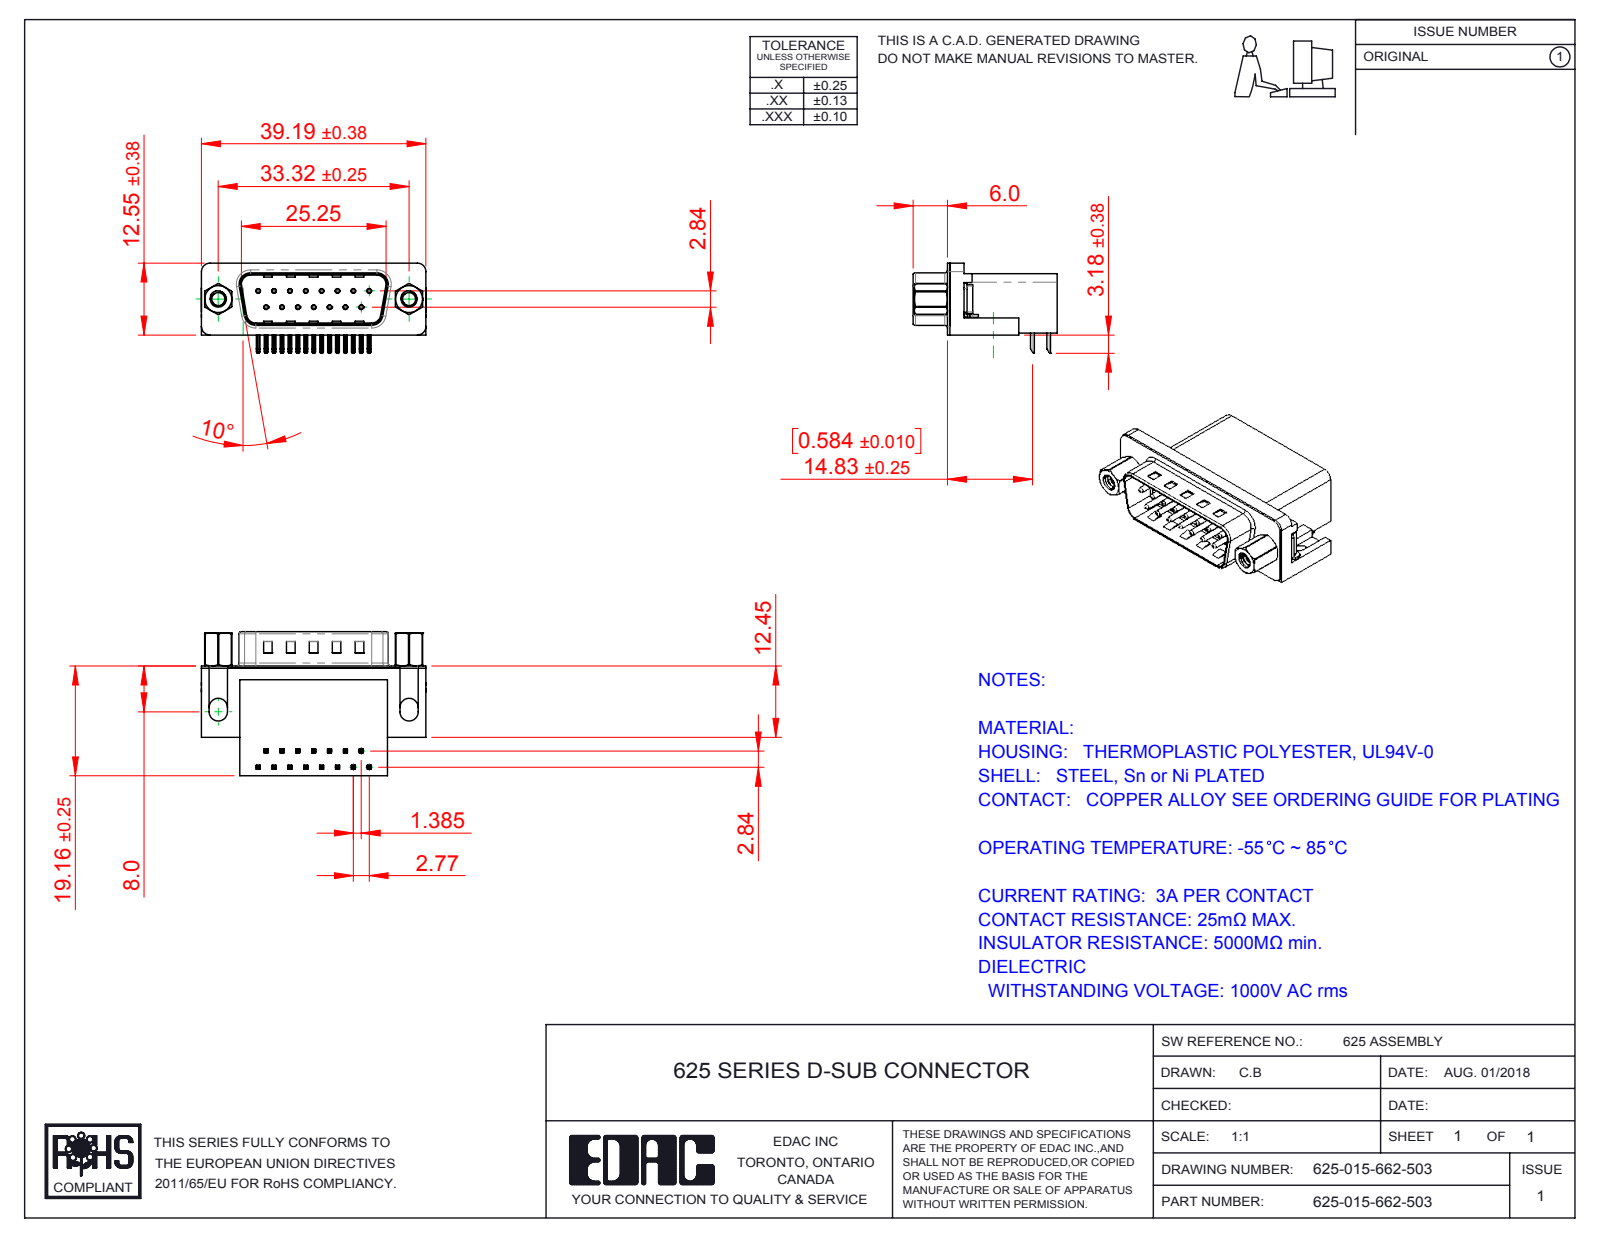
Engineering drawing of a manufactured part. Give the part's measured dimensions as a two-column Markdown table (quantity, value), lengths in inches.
| quantity | value |
| --- | --- |
| part name | 625-015-662-503; 625 Shell_15 Socket; 625 4-40 Hex Standoff 5; 625 Non Board Mount (+4 more) |
| STEP written by | SolidWorks 2016 (CONFIG_CONTROL_DESIGN) |
| units | inches |
| bodies | 23 solids, 1603 faces (917 planar, 515 cylindrical, 171 other) |
| overall size | 1.544 × 0.991 × 0.619 |
| volume | 0.392 in³ |
| surface area | 10.5 in² |
| round holes (diameter × count) | 0.014 × 15, 0.031 × 15, 0.089 × 2, 0.09 × 2, 0.157 × 2, 0.189 × 2, 0.197 × 2 |
| round bosses / shafts (diameter × count) | 0.03 × 15, 0.193 × 2, 0.187 × 2, 0.154 × 2, 0.11 × 2 |
| partial cylindrical surfaces (radius × count) | 0.01 × 68, 0.005 × 30, 0.039 × 16, 0.02 × 9, 0.063 × 8, 0.059 × 6, 0.035 × 4, 0.079 × 4 |
| main face-to-face distances | 0.016, 0.407, 0.739, 0.083, 0.754, 0.412, 0.067, 0.428, 0.345, 0.64 |
| hole center spacings | 0.124, 0.109, 0.218, 0.327, 0.436, 0.198, 0.198, 0.294 |
